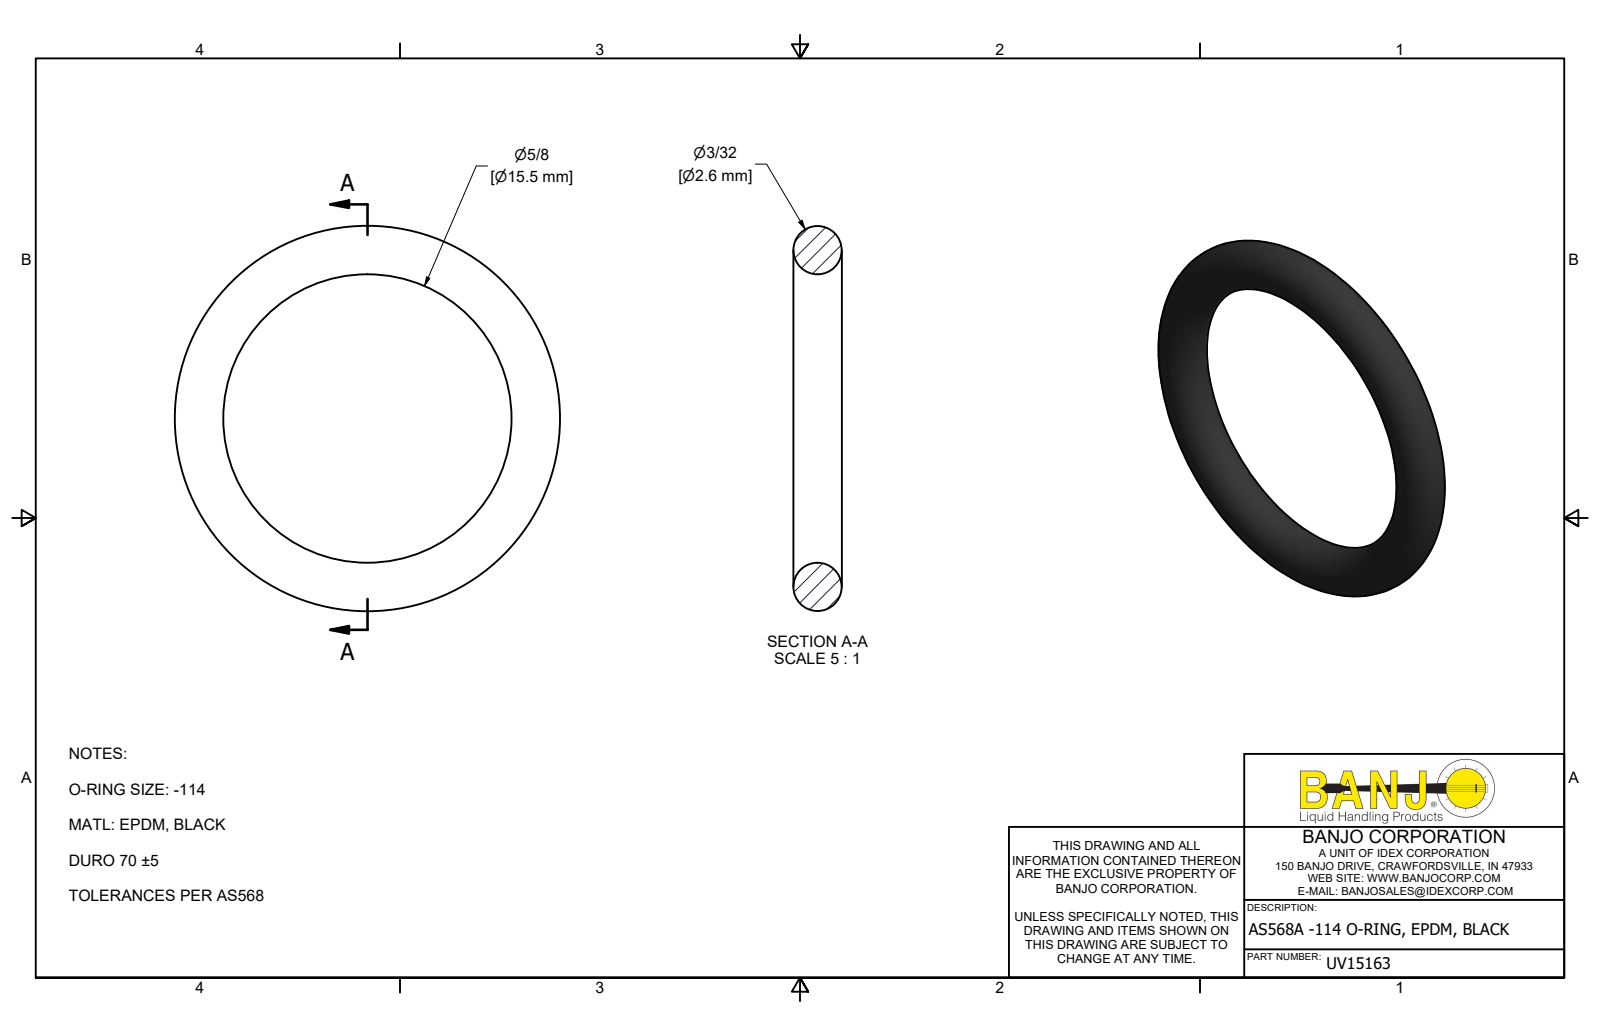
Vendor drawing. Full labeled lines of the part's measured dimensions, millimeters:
Part name (STEP PRODUCT): UV15163
STEP written by: Autodesk Inventor 2022 (AUTOMOTIVE_DESIGN)
Units: millimetres
Bodies: 1 solid, 1 faces (0 planar, 0 cylindrical, 1 other)
Overall size (bounding box): 20.8 × 20.8 × 2.6
Volume: 310 mm³ · Surface area: 469 mm²
